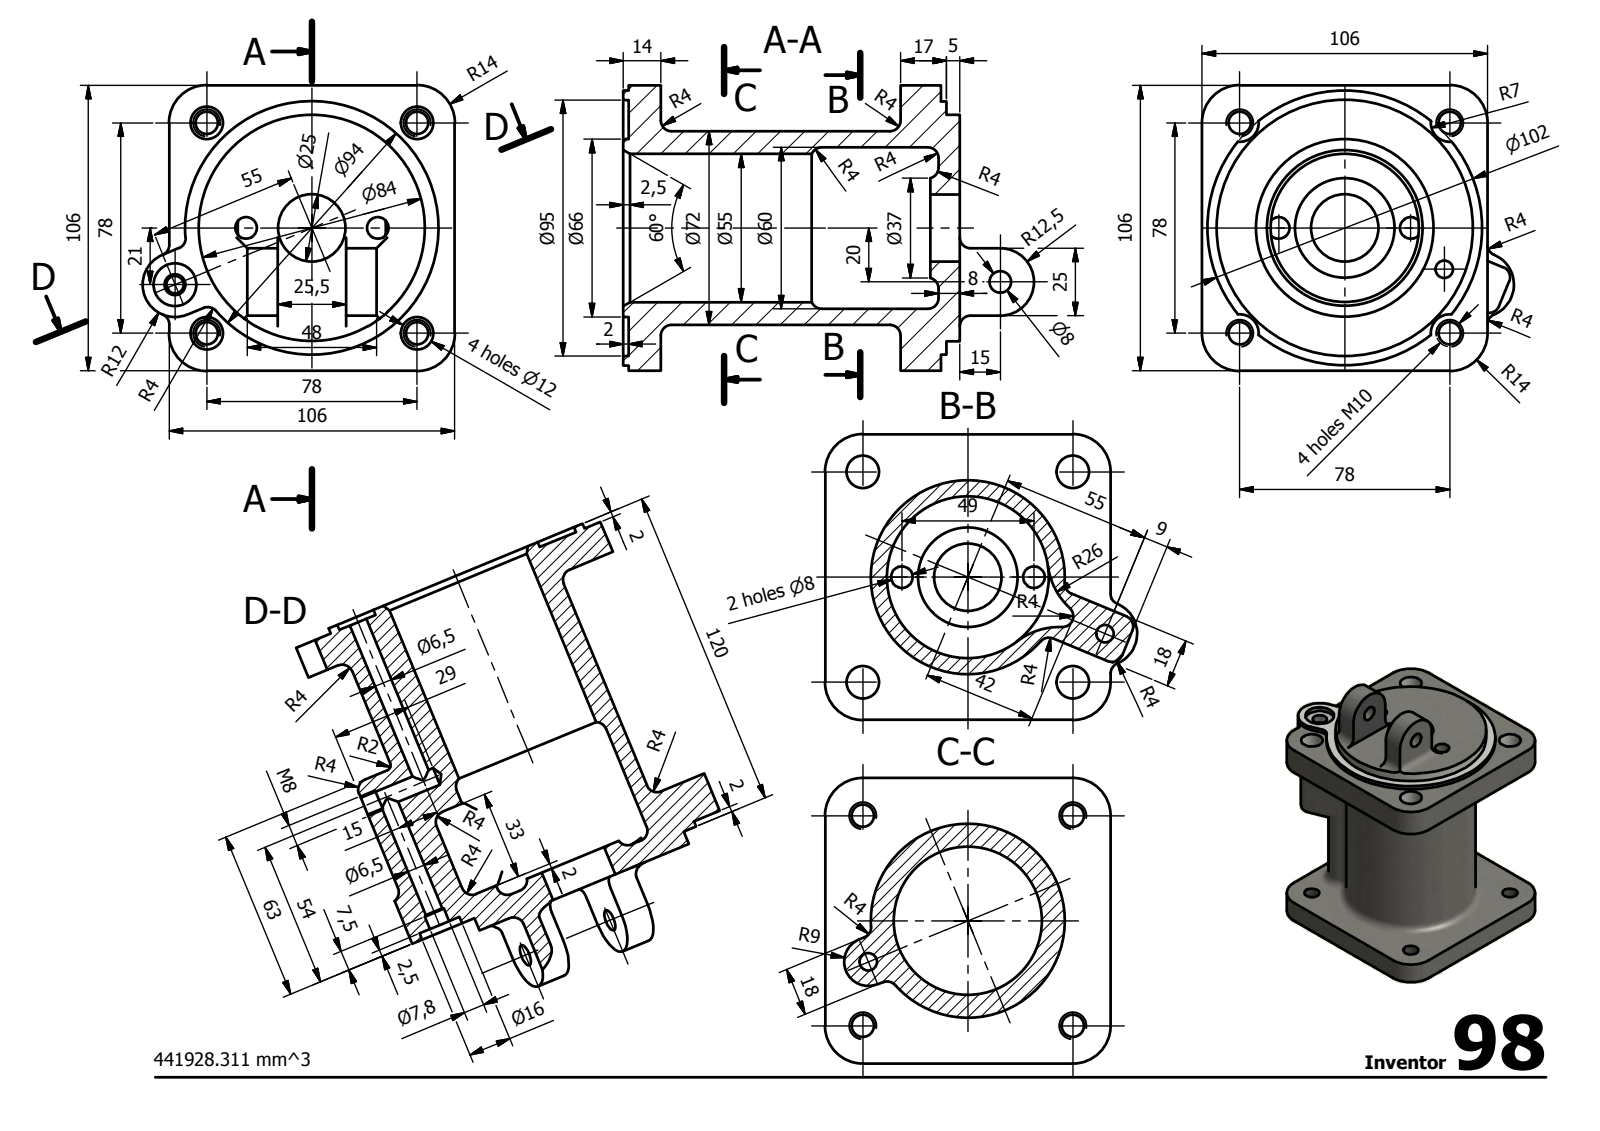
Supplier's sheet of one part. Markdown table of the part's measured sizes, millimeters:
| quantity | value |
| --- | --- |
| STEP written by | Autodesk Inventor 2014 (AUTOMOTIVE_DESIGN) |
| units | millimeters |
| bodies | 1 solid, 135 faces (38 planar, 71 cylindrical, 26 other) |
| overall size | 152.5 × 115.83 × 106 |
| volume | 441 929 mm³ |
| surface area | 103 747 mm² |
| round holes (diameter × count) | 8.38 × 4, 12 × 4, 8 × 3, 6.5 × 2, 6.65 × 1, 7.8 × 1, 16 × 1, 25 × 1, 55 × 1, 60 × 1, 95 × 1 |
| round bosses / shafts (diameter × count) | 102 × 1, 94 × 1, 84 × 1, 72 × 1, 66 × 1 |
| partial cylindrical surfaces (radius × count) | 4 × 21, 7 × 4, 14 × 4, 26 × 2, 9 × 1, 12 × 1, 12.5 × 1 |
| main face-to-face distances | 12, 106, 101, 89, 22, 123, 111, 2, 116, 104 |
| hole center spacings | 41.61, 55.15, 74.52, 78, 24.5, 110.31, 15, 19.71 |
